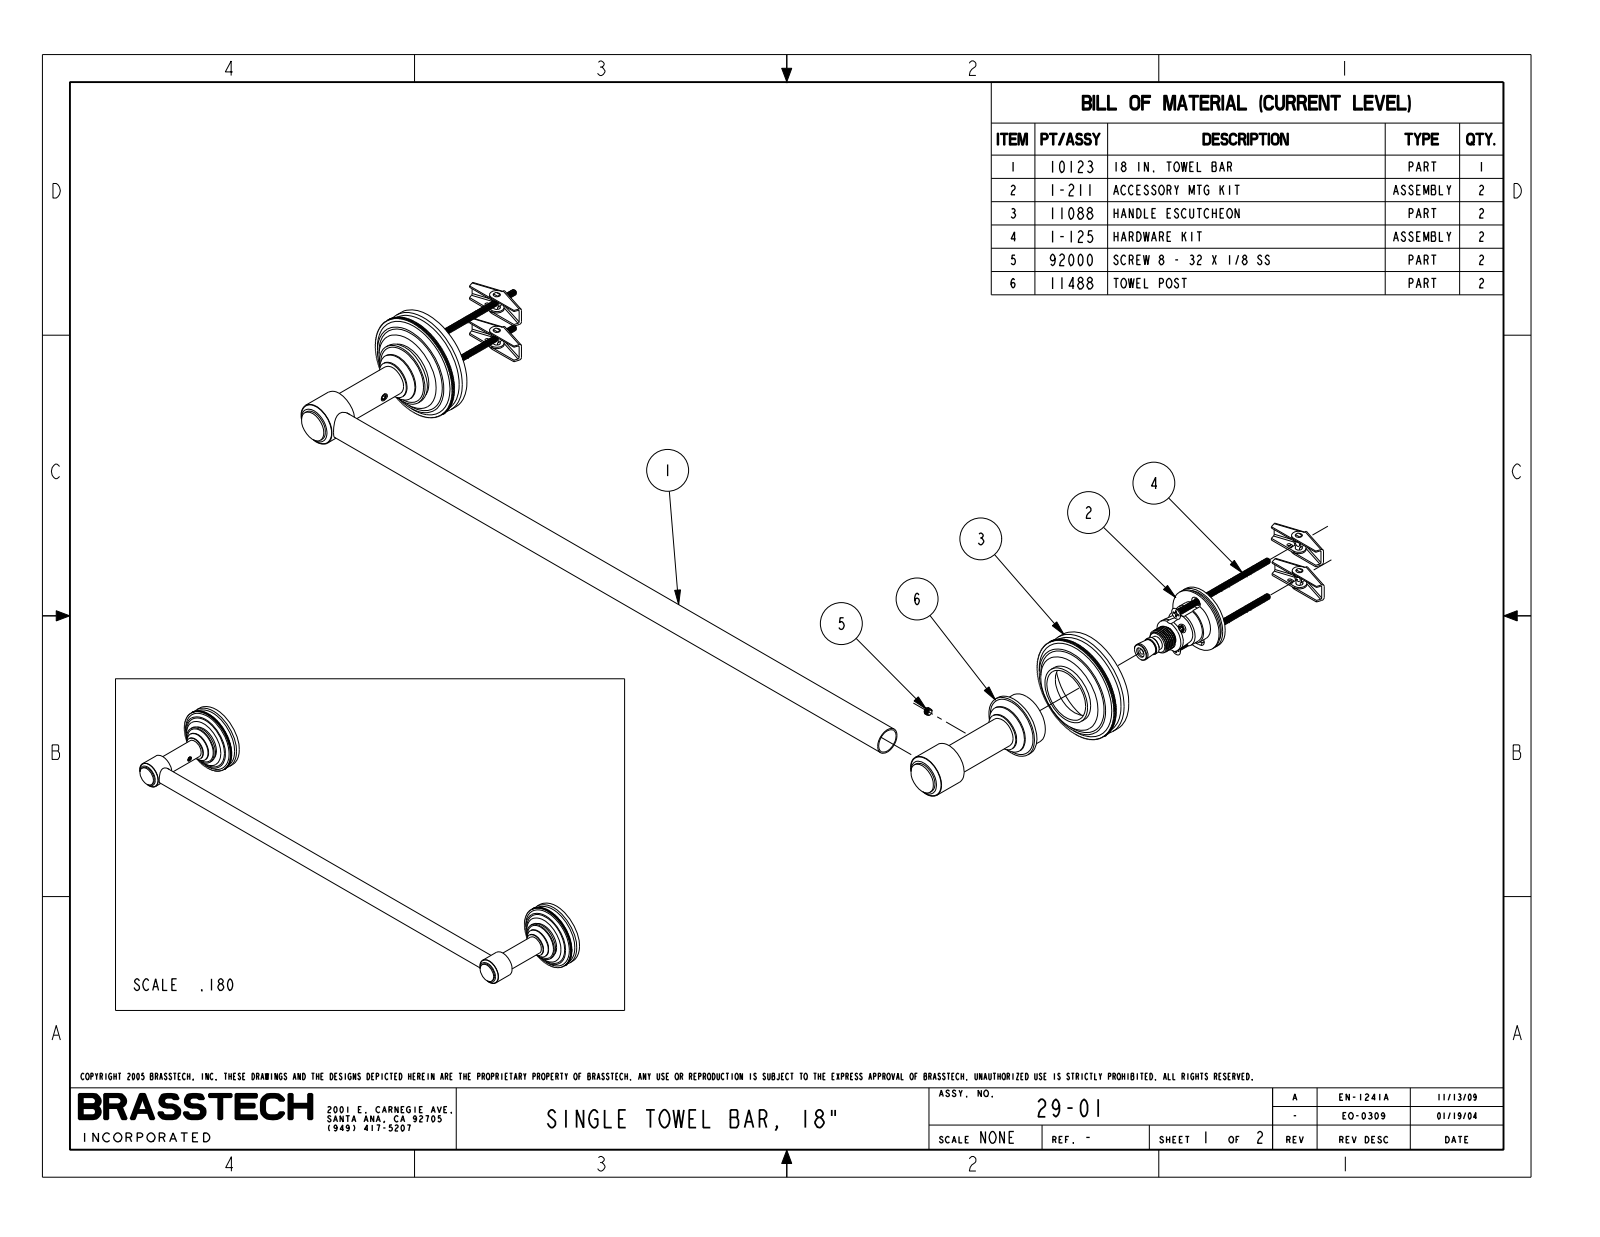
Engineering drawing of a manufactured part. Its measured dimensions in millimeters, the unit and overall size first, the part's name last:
Units: millimetres
Overall size (bounding box): 530.2 × 95.3 × 63.5
Round bosses / shafts (diameter × count): ⌀63.5 ×2, ⌀61 ×2, ⌀37.6 ×2, ⌀35.1 ×2, ⌀28.8 ×2, ⌀25.4 ×2, ⌀22.4 ×2, ⌀18.4 ×2
Main face-to-face distances: 2.5, 12.1, 10.2, 1.9, 5.1, 14.6, 4.4, 17.1, 7, 1.9
Bodies: 0 solids, 996 faces (564 planar, 398 cylindrical, 34 other)
Part name (STEP PRODUCT): 29-01_WEB
STEP written by: PRO/ENGINEER BY PARAMETRIC TECHNOLOGY CORPORATION, 2009300 (CONFIG_CONTROL_DESIGN)
